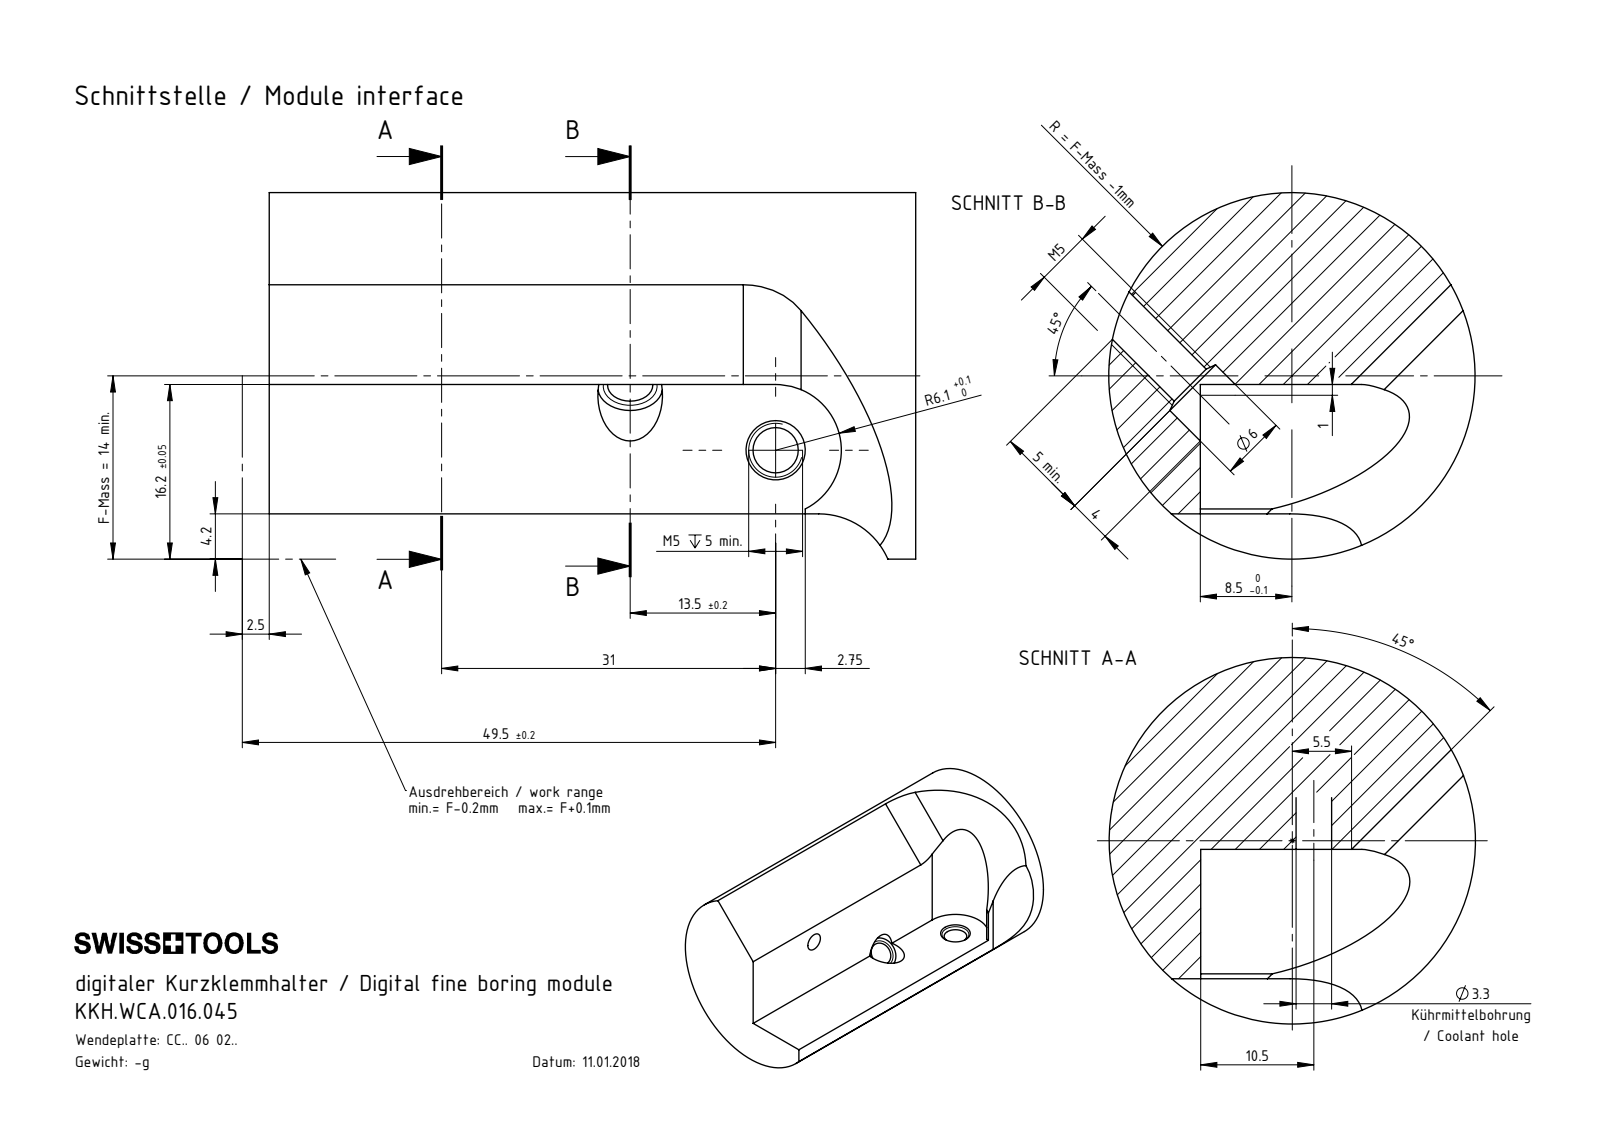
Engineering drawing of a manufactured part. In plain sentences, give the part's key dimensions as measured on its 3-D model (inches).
The part is named "WCA-ER2.001.006_A; Fxx-MAB.xxx.xxx_A_F20M1x2; KKH-ER3.012.007_A; KKH-ER1.014.045_B (+8 more)". Its 3-D file was written by "SolidWorks 2017 (AUTOMOTIVE_DESIGN)". It is 13 solids with 495 faces: 262 planar, 138 cylindrical and 95 other. Overall it measures 2.185 by 0.791 by 0.767 inches. Its volume is 0.444 cubic inches and its surface area 12.02 square inches. Round holes: 3 of diameter 0.098, 2 of diameter 0.083, 2 of diameter 0.118, 1 of diameter 0.081, 1 of diameter 0.11, 1 of diameter 0.13, 1 of diameter 0.144, 1 of diameter 0.152, 1 of diameter 0.165, 1 of diameter 0.217, 1 of diameter 0.409, 1 of diameter 0.415. Round bosses or shafts: 6 of diameter 0.075, 2 of diameter 0.197, 1 of diameter 0.472, 1 of diameter 0.394, 1 of diameter 0.374, 1 of diameter 0.157, 1 of diameter 0.134, 1 of diameter 0.118. Partial cylindrical surfaces (rounded edges, fillets, slot ends): 14 of radius 0.063, 6 of radius 0.008, 5 of radius 0.014, 4 of radius 0.043, 3 of radius 0.047, 2 of radius 0.039, 2 of radius 0.079, 2 of radius 0.108. The main face-to-face distances are 0.197, 0.339, 0.142, 0.11, 0.213, 0.126, 0.445, 0.016, 0.323, 0.551. The hole center spacings are 0.614, 0.85, 0.866, 0.906, 0.906, 1.772, 0.136, 0.146.
